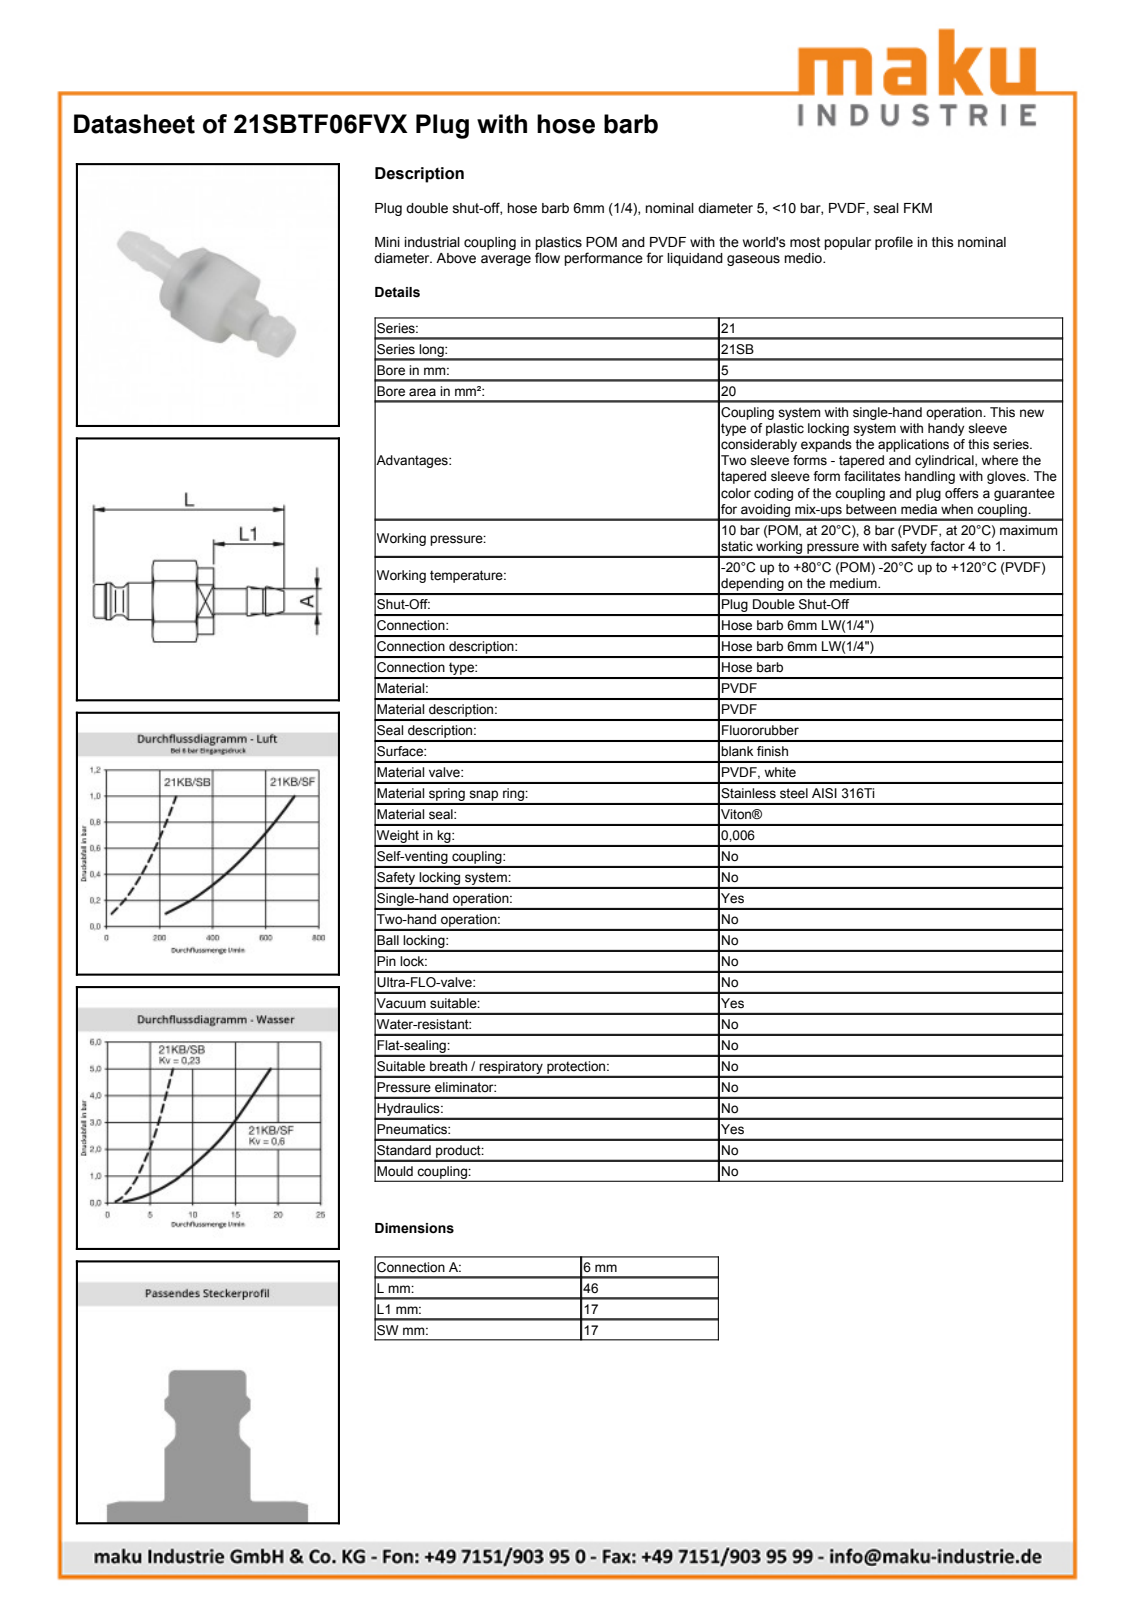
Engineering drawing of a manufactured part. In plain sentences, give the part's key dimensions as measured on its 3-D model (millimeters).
The part is named "D105879". Its 3-D file was written by "Autodesk Inventor 2011 (AUTOMOTIVE_DESIGN)". It is 1 solid with 60 faces: 15 planar, 16 cylindrical and 29 other. Overall it measures 50 by 15.62 by 15.14 millimeters. Its volume is 4 264 cubic millimeters and its surface area 2 159 square millimeters. Round holes: 1 of diameter 12. Round bosses or shafts: 1 of diameter 14, 1 of diameter 11.09, 1 of diameter 9, 1 of diameter 8.1, 1 of diameter 6.7, 1 of diameter 6.05. Partial cylindrical surfaces (rounded edges, fillets, slot ends): 1 of radius 7.9. The main face-to-face distances are 14, 18.9, 14.1, 33, 25, 8, 17, 10.9, 50, 35.9.
